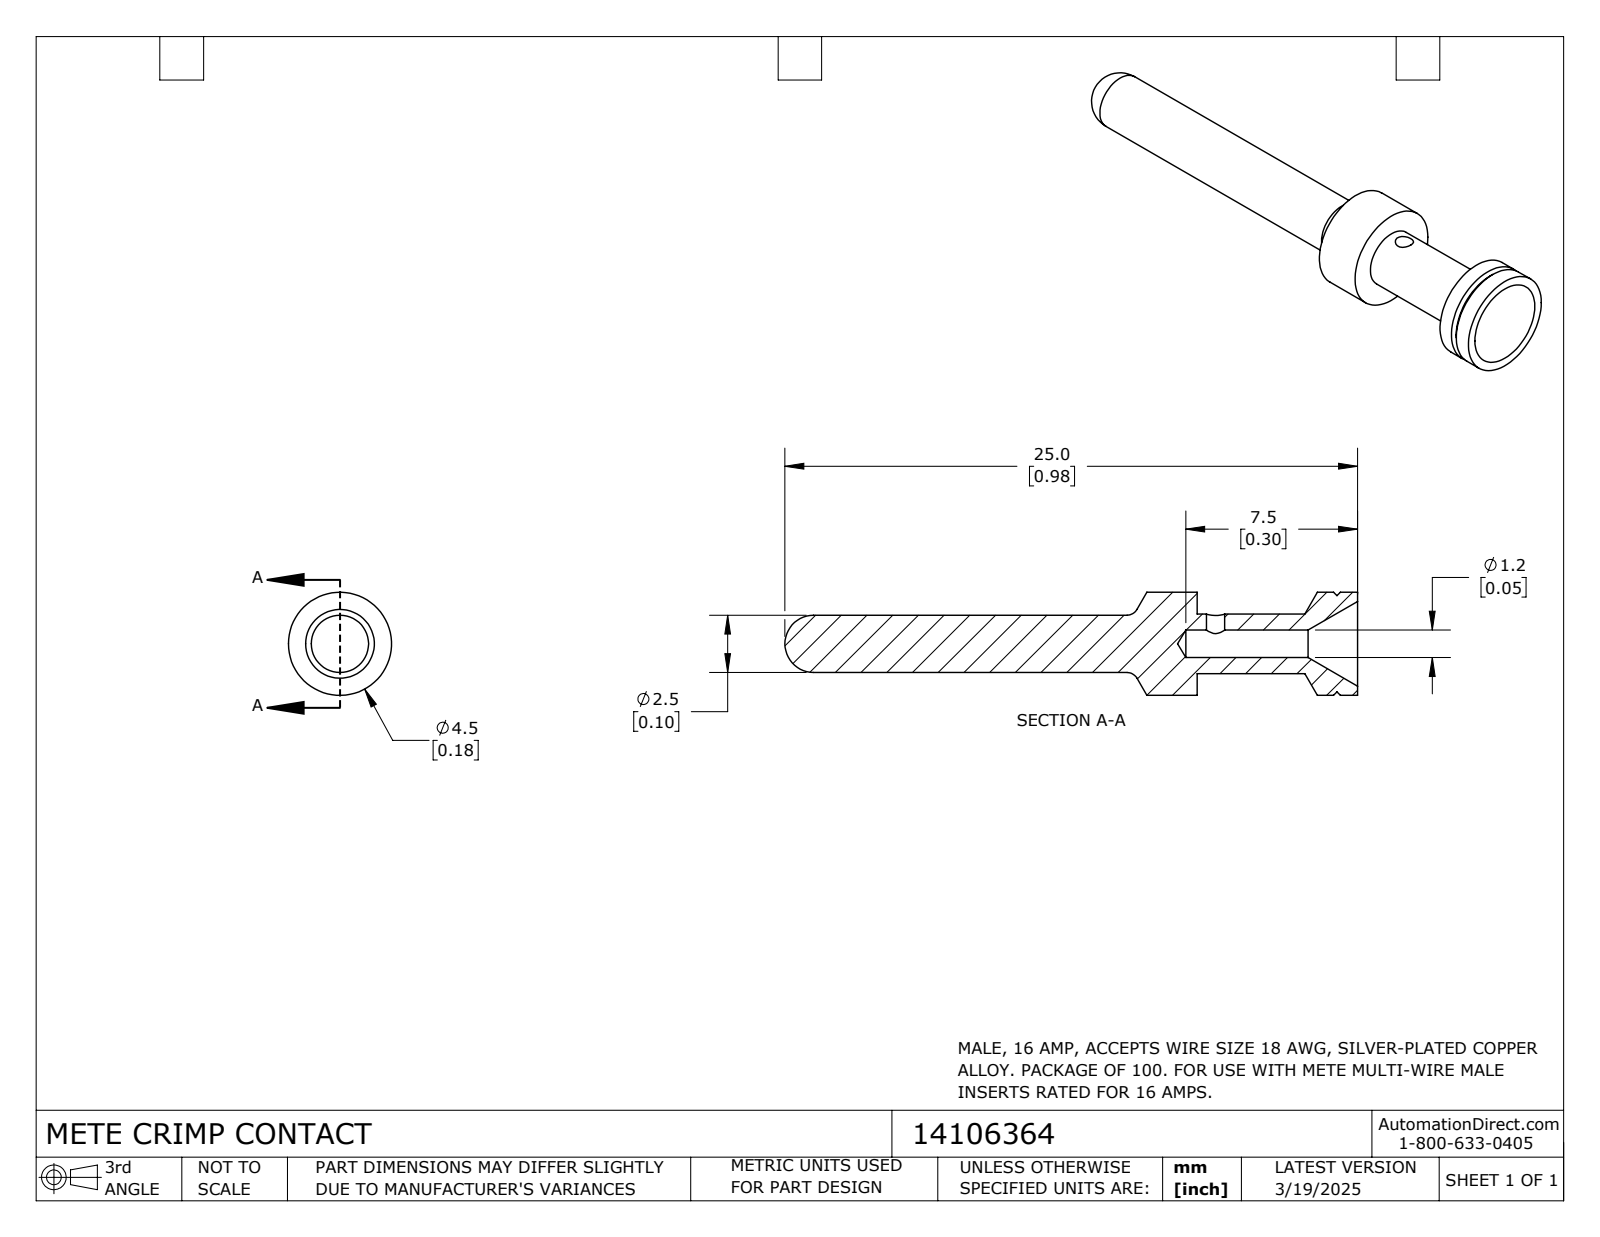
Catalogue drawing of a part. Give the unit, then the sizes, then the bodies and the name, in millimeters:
Units: millimetres
Overall size (bounding box): 25 × 4.5 × 4.5
Round holes (diameter × count): ⌀0.8 ×1, ⌀1.2 ×1
Round bosses / shafts (diameter × count): ⌀4.5 ×1, ⌀2.6 ×1, ⌀2.5 ×1
Main face-to-face distances: 7
Volume: 154 mm³ · Surface area: 297 mm²
Bodies: 1 solid, 32 faces (2 planar, 14 cylindrical, 16 other)
Part name (STEP PRODUCT): 14106364
STEP written by: SolidWorks 2024 (CONFIG_CONTROL_DESIGN)
